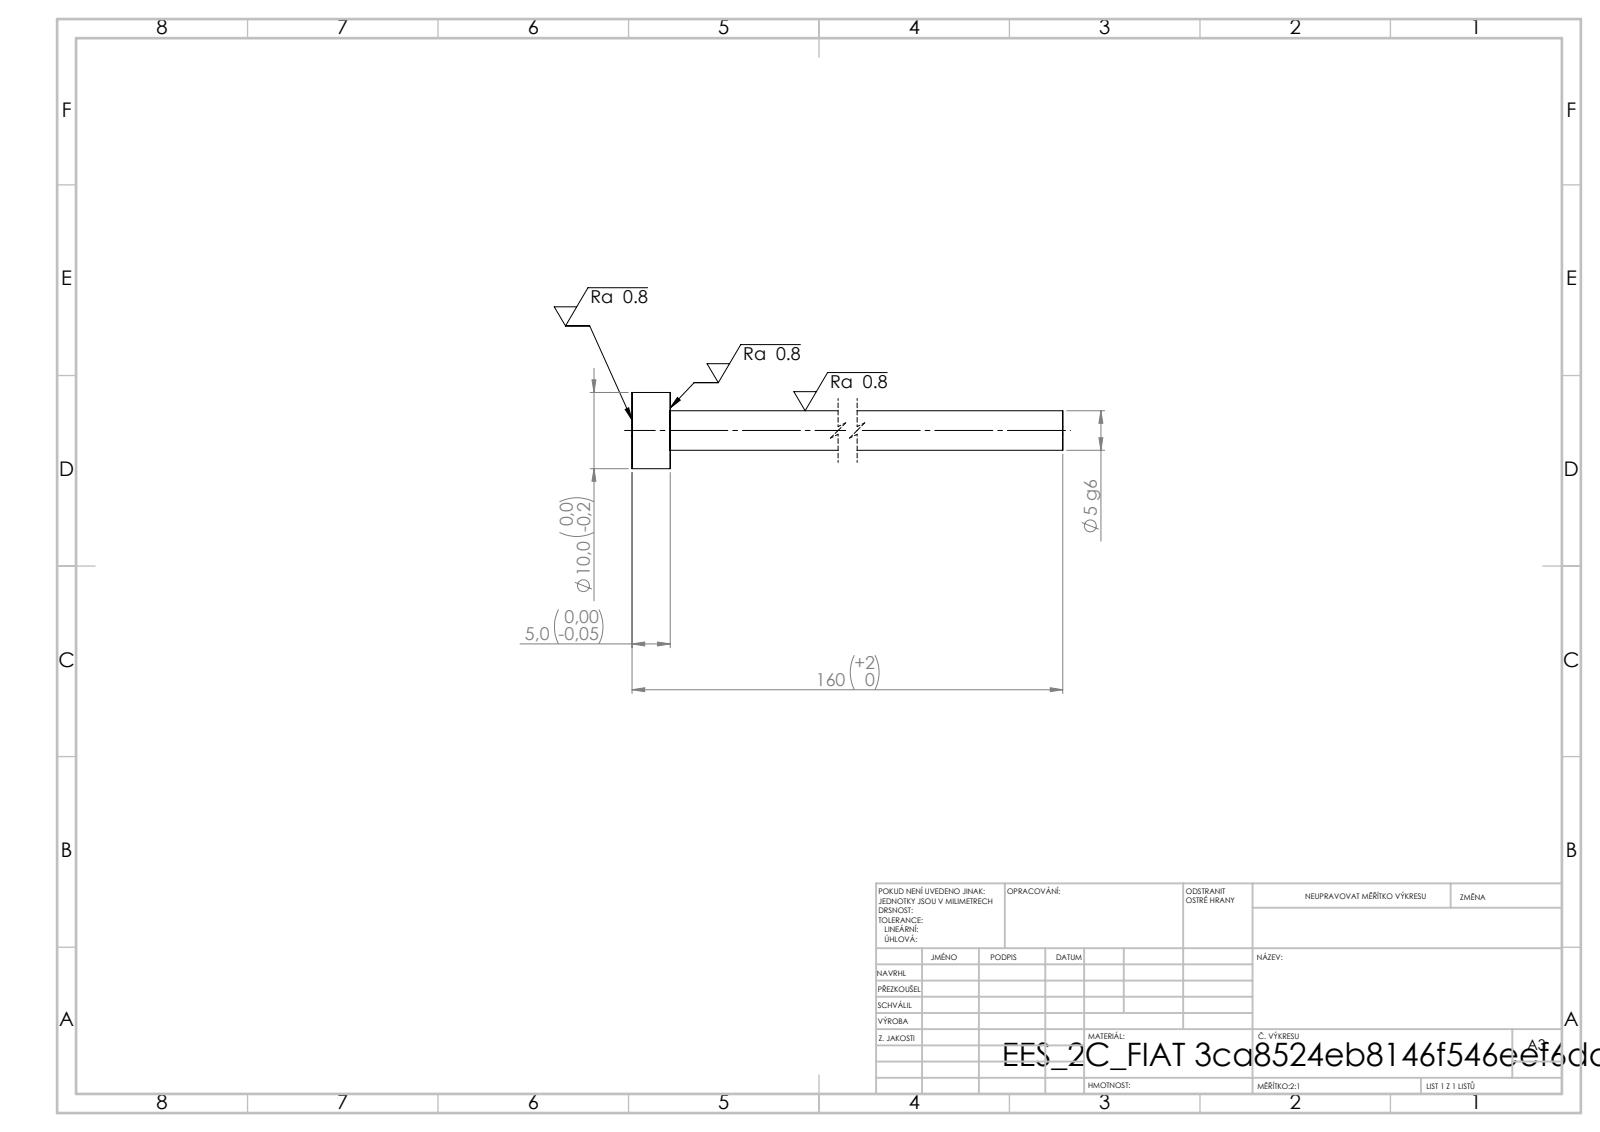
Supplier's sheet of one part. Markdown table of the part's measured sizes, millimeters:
| quantity | value |
| --- | --- |
| STEP written by | SolidWorks 2019 (CONFIG_CONTROL_DESIGN) |
| units | millimeters |
| bodies | 1 solid, 7 faces (3 planar, 4 cylindrical, 0 other) |
| overall size | 160 × 10 × 10 |
| volume | 3 684 mm³ |
| surface area | 2 846 mm² |
| round bosses / shafts (diameter × count) | 10 × 1, 5.2 × 1 |
| main face-to-face distances | 5, 160, 155 |
